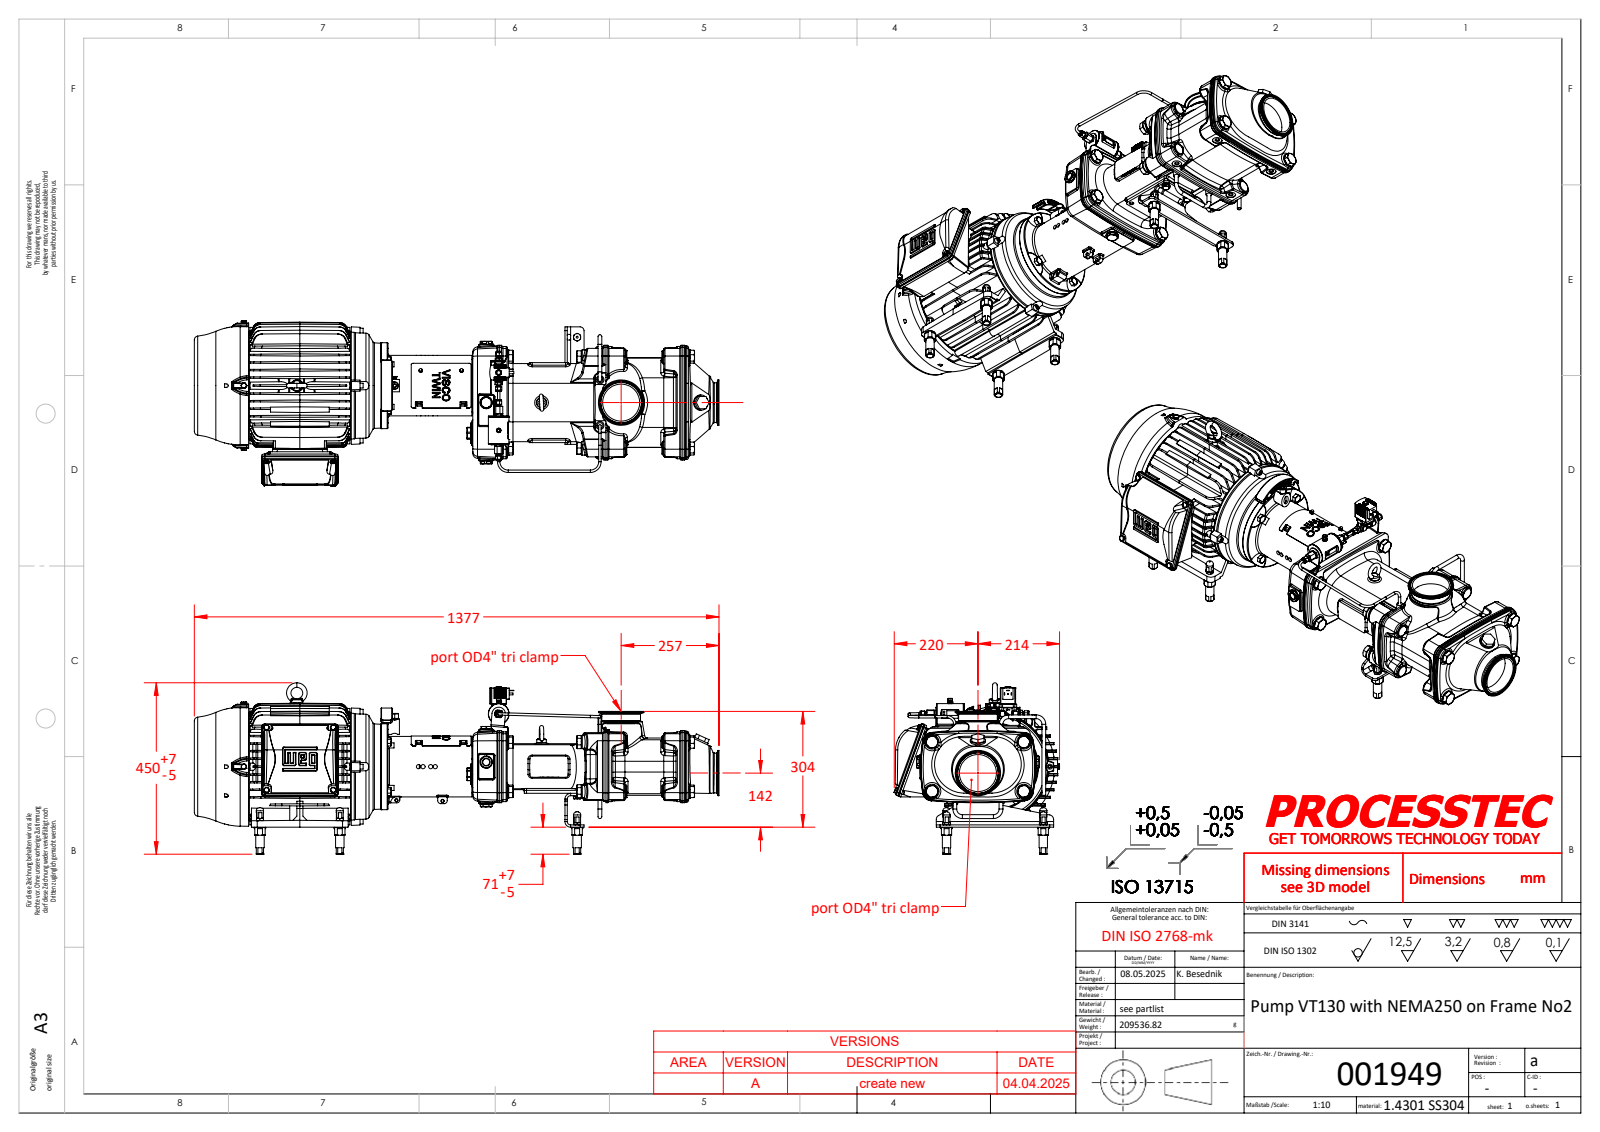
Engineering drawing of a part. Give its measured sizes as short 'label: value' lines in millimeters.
name: 001485; 001727; 001073; 001031_ISO 4017 - M10 X 25 - A2-70 (+8 more)
written by: SolidWorks 2023 (AUTOMOTIVE_DESIGN)
unit: mm
bodies: 112 solids, 8803 faces (2873 planar, 2320 cylindrical, 3610 other)
size: 1377.35 × 449.75 × 434.2
volume: 58 270 000 mm³; area: 3 732 000 mm²
holes: 9× ⌀8, 9× ⌀8.5, 9× ⌀17.5, 7× ⌀6, 7× ⌀10.2, 6× ⌀5.9, 6× ⌀7.2, 6× ⌀12, 6× ⌀14, 6× ⌀14.5, 6× ⌀22.2, 5× ⌀4.1
bosses: 10× ⌀30, 10× ⌀10, 9× ⌀8, 7× ⌀22, 7× ⌀11.6, 6× ⌀20, 6× ⌀19, 6× ⌀7
rounds: 242× R3, 42× R1.5, 39× R2, 27× R1.2, 25× R5, 25× R6, 23× R7, 23× R8
face distances: 19.8, 39.6, 265.9, 14, 5.8, 121.2, 657.25, 391.35, 481, 141
hole spacings: 55, 129.3, 41.49, 94.26, 118.86, 145.91, 28.75, 56.56
